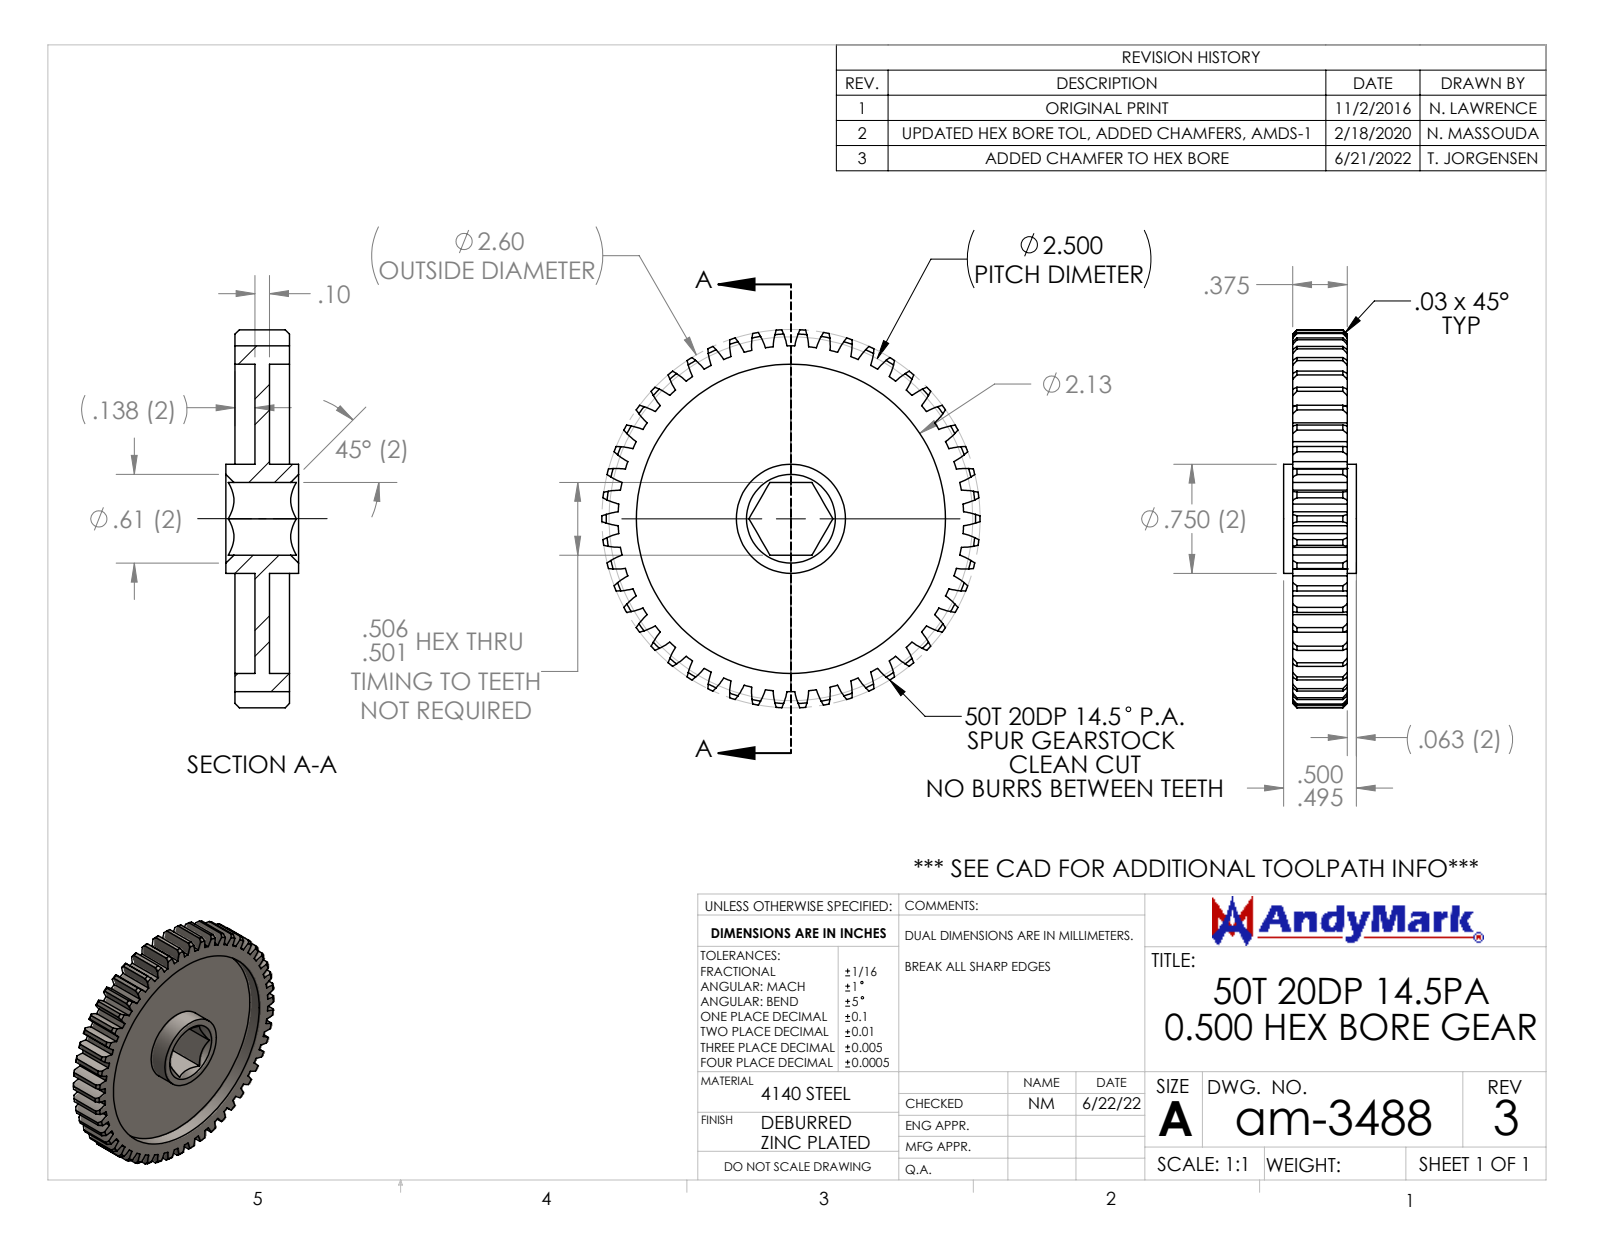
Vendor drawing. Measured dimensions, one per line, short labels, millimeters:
name: am-3488 50T 20DP 500hex 375 FW
written by: SolidWorks 2021 (CONFIG_CONTROL_DESIGN)
unit: mm
bodies: 1 solid, 329 faces (12 planar, 213 cylindrical, 104 other)
size: 66 × 66 × 12.7
volume: 14 800 mm³; area: 12 110 mm²
holes: 1× ⌀54
bosses: 1× ⌀19.1
rounds: 100× R12.7, 1× R30.2, 1× R33
face distances: 2.5, 3.5, 6, 9.5, 6, 3.5, 12.7, 5.1, 7.6, 1.6
